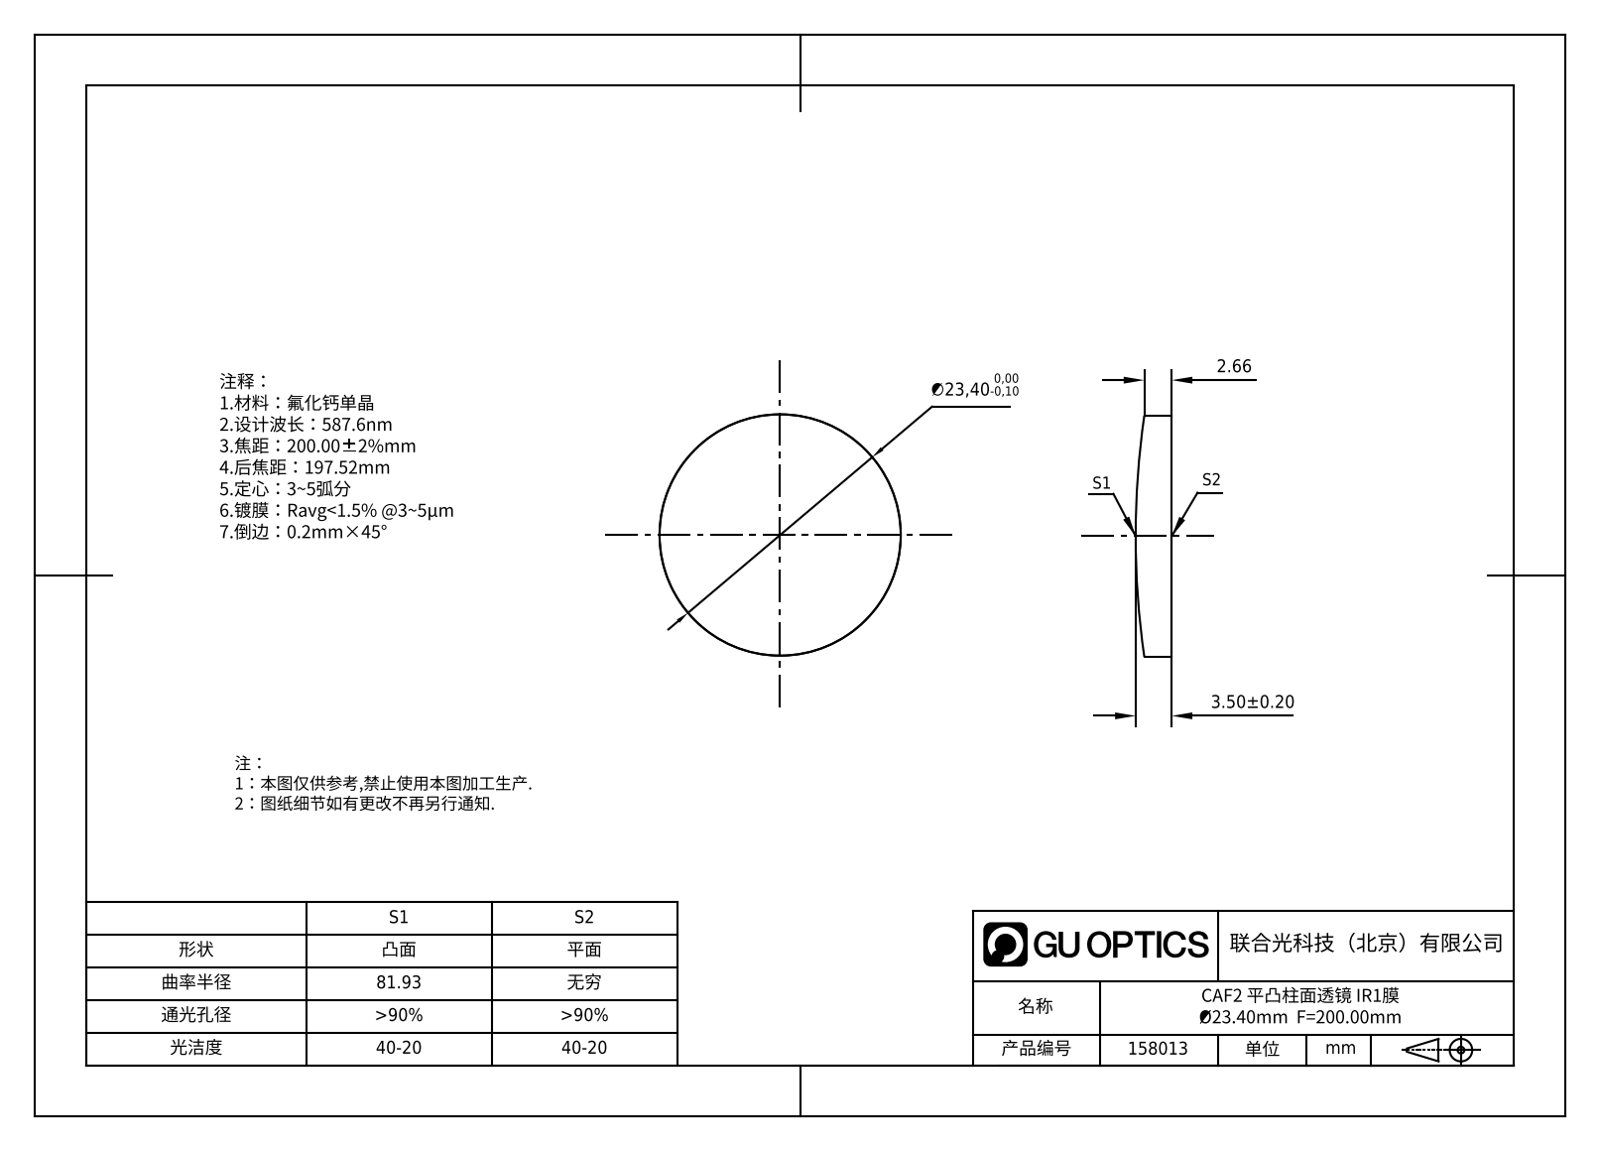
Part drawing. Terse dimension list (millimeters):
name: GL55-025-200-IR1
written by: SolidWorks 2022 (AUTOMOTIVE_DESIGN)
unit: mm
bodies: 1 solid, 9 faces (1 planar, 4 cylindrical, 4 other)
size: 23.4 × 23.4 × 3.5
volume: 1 411 mm³; area: 1 071 mm²
bosses: 1× ⌀23.4
rounds: 1× R81.93
